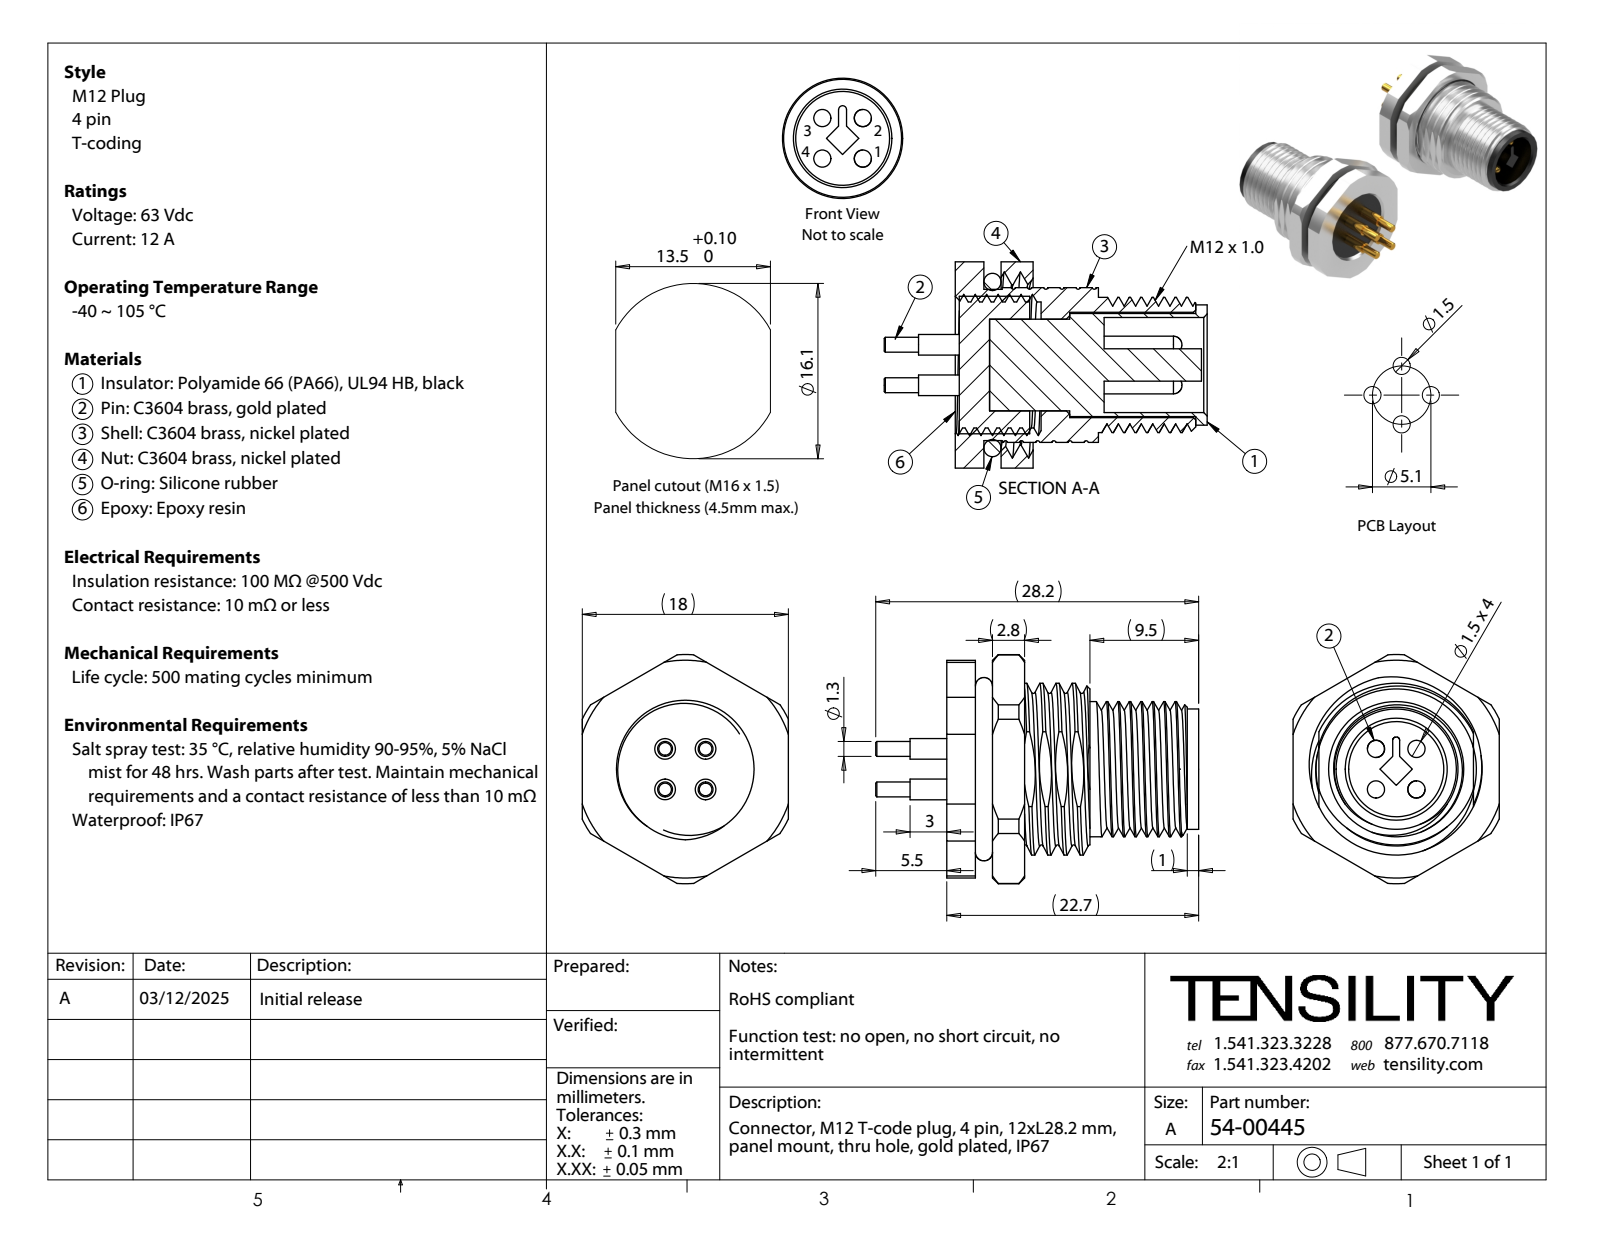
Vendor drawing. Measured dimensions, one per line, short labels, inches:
name: 54-00445-04; 54-00445-03; 54-00445-02; 54-00445 (+3 more)
written by: SolidWorks 2021 (CONFIG_CONTROL_DESIGN)
unit: in
bodies: 9 solids, 326 faces (81 planar, 149 cylindrical, 96 other)
size: 1.11 × 0.787 × 0.709
volume: 0.189 in³; area: 9.054 in²
holes: 4× ⌀0.059, 1× ⌀0.315, 1× ⌀0.327, 1× ⌀0.362, 1× ⌀0.433, 1× ⌀0.551
bosses: 4× ⌀0.071, 4× ⌀0.051, 1× ⌀0.52, 1× ⌀0.472, 1× ⌀0.465, 1× ⌀0.413, 1× ⌀0.354
rounds: 1× R0.012, 1× R0.295, 1× R0.374, 1× R0.394
face distances: 0.098, 0.709, 0.039, 0.157, 0.138, 0.02, 0.118, 0.256, 0.394, 0.169
hole spacings: 0.098, 0.139, 0.197
